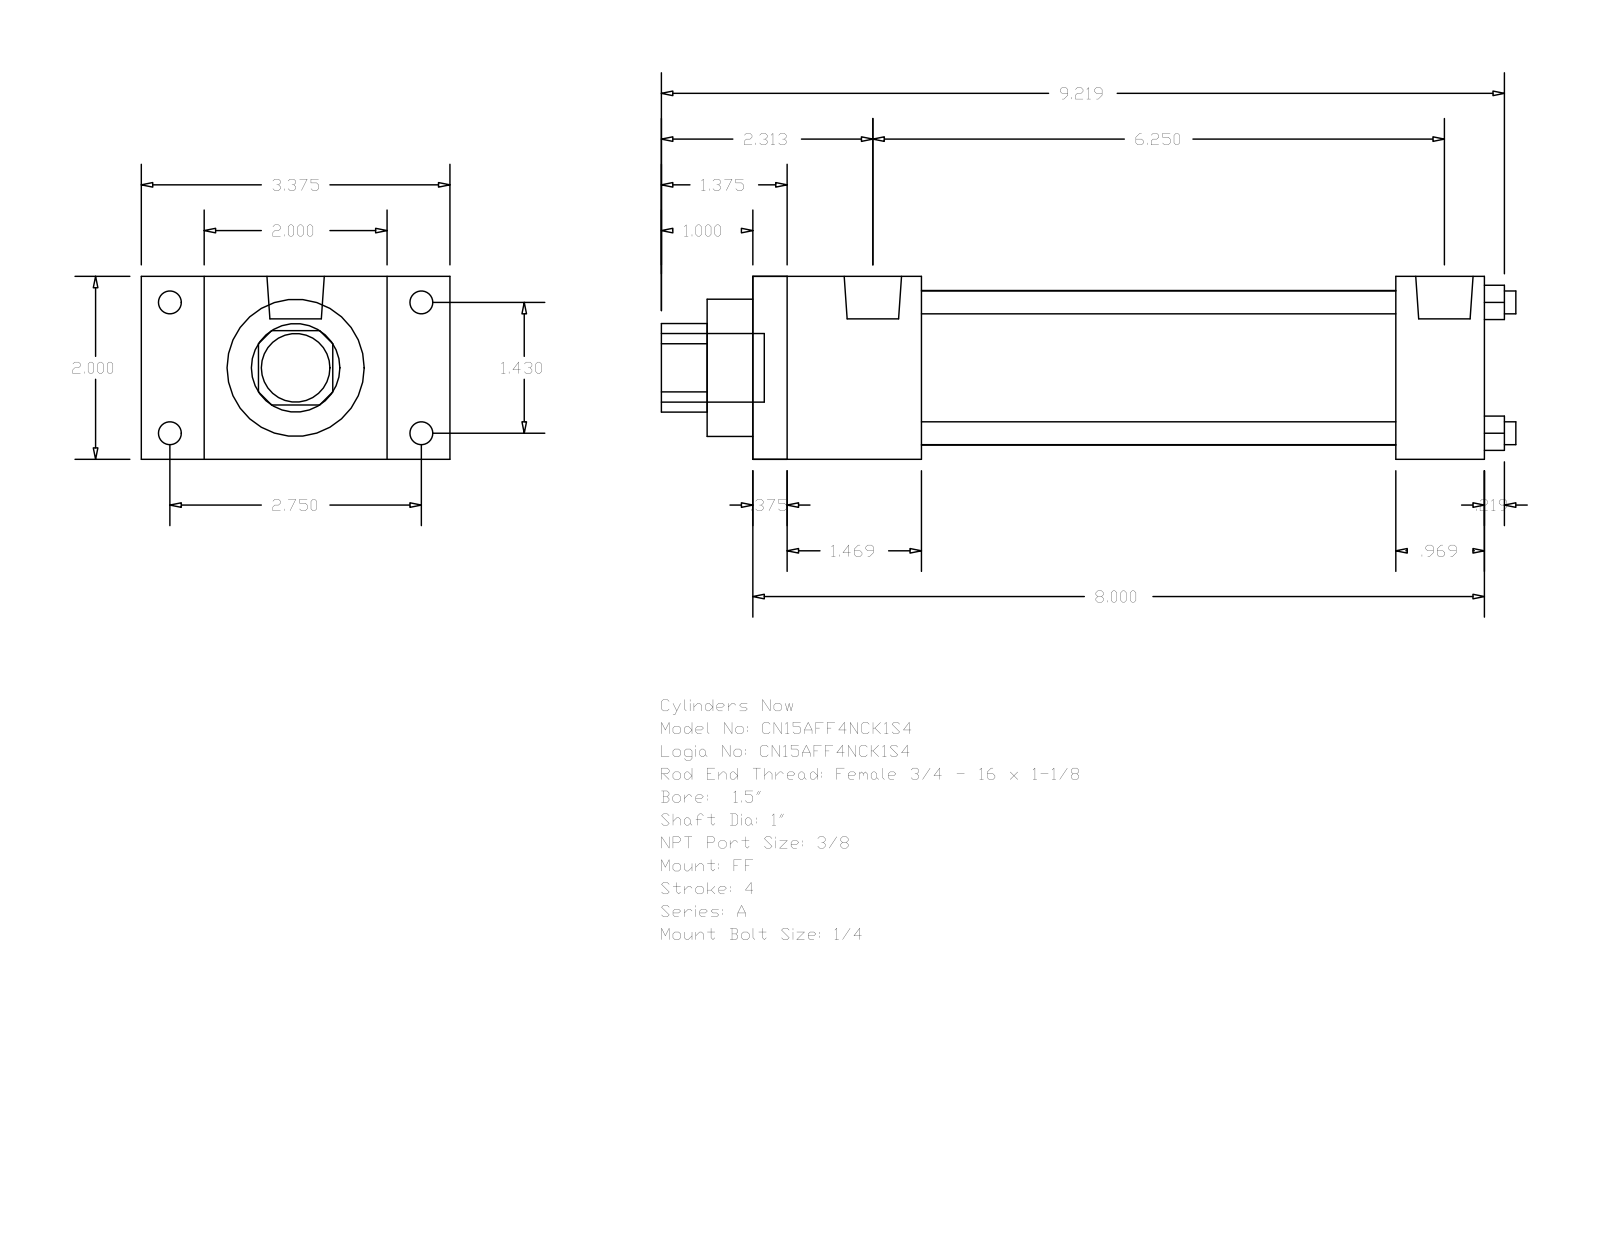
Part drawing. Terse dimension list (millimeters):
name: A_FF__0150_1
written by: GSSL Pune (CONFIG_CONTROL_DESIGN)
unit: mm
bodies: 0 solids, 92 faces (64 planar, 28 cylindrical, 0 other)
size: 237.33 × 85.72 × 50.8
holes: 4× ⌀6.35, 1× ⌀25.4, 1× ⌀38.1, 1× ⌀42.93
bosses: 4× ⌀6.35, 4× ⌀5.56, 2× ⌀15.93, 1× ⌀19.05
rounds: 1× R12.29
face distances: 50.8, 203.2, 9.52, 193.68, 46.83, 178.59, 37.31, 169.07, 131.76, 156.37
hole spacings: 25.68, 36.32, 51.36
